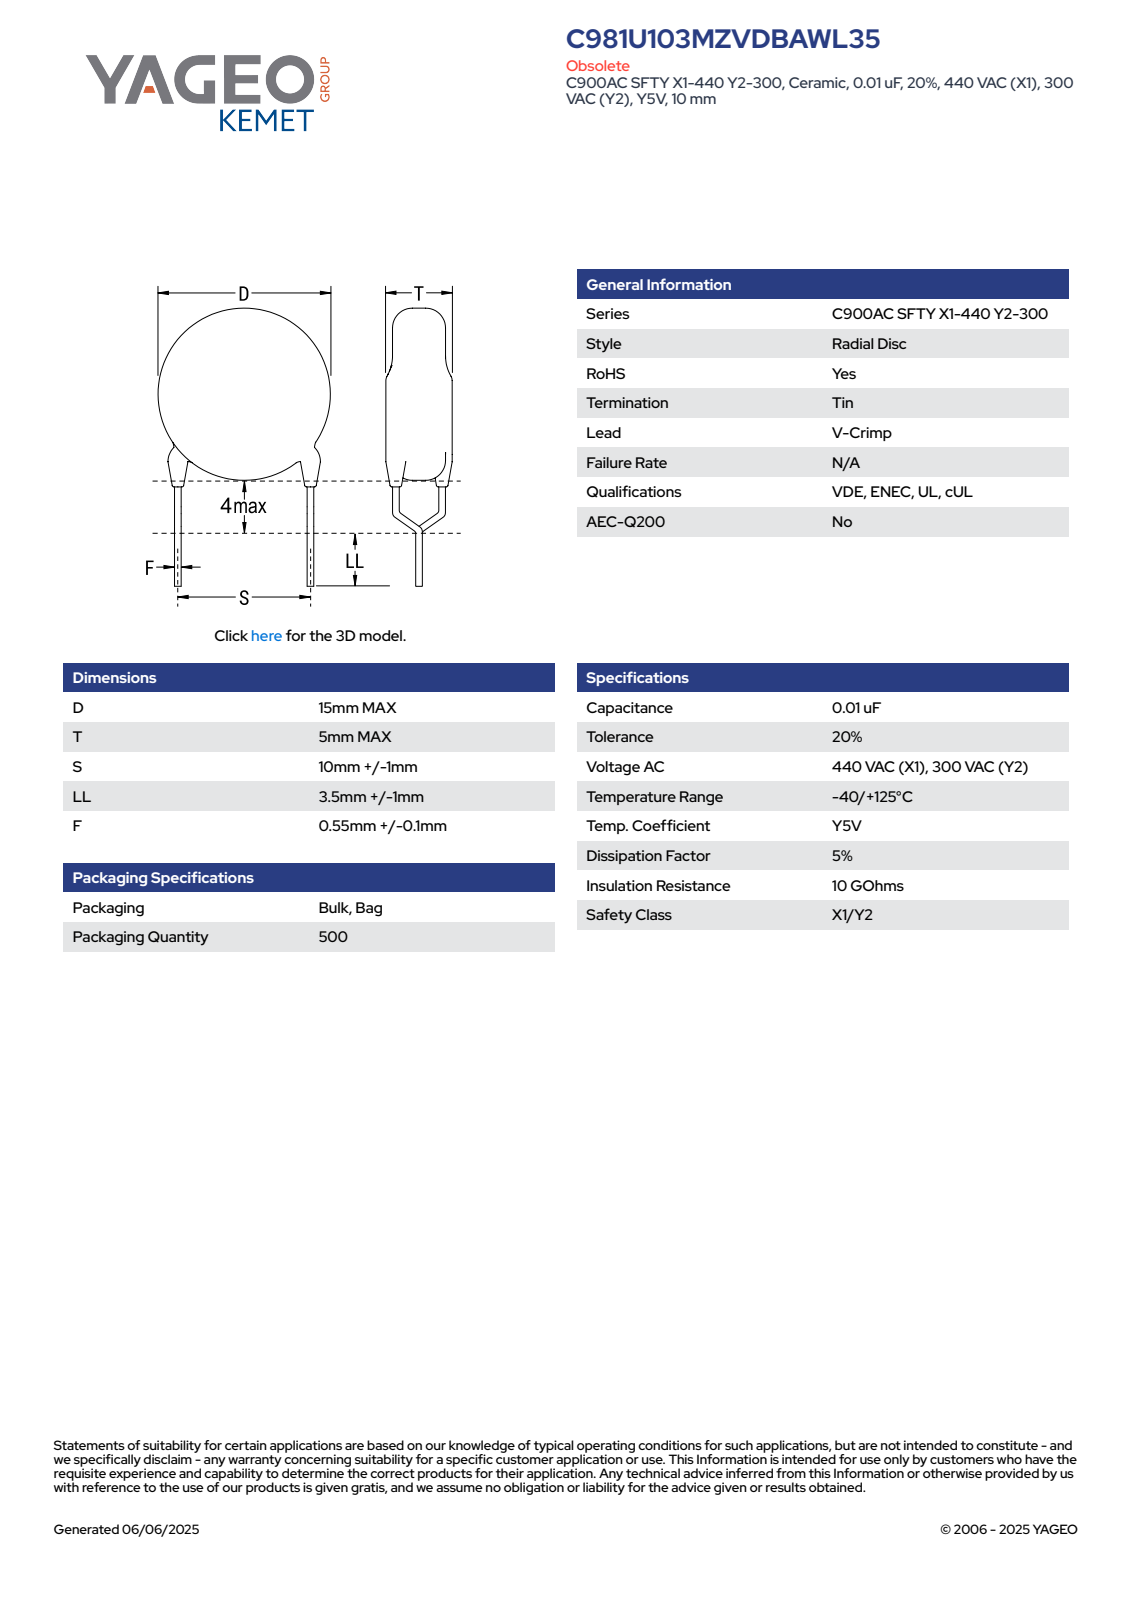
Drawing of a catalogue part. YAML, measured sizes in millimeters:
part_name: "CCD_VCC900_D15T5S10LL4.5F0.65"
step_written_by: "SolidWorks 2014 (AUTOMOTIVE_DESIGN)"
units: millimeters
bodies: {solids: 5, faces: 93, planar: 65, cylindrical: 16, other: 12}
overall_size: [23.3, 15, 5]
volume: 873
surface_area: 616
round_bosses_or_shafts:
  - {diameter: 0.65, count: 6}
  - {diameter: 15, count: 1}
face_to_face_distances: [5, 7.4, 16.77, 9.37, 14.82, 7.42, 1.95, 0.53, 7.96, 0.37]
